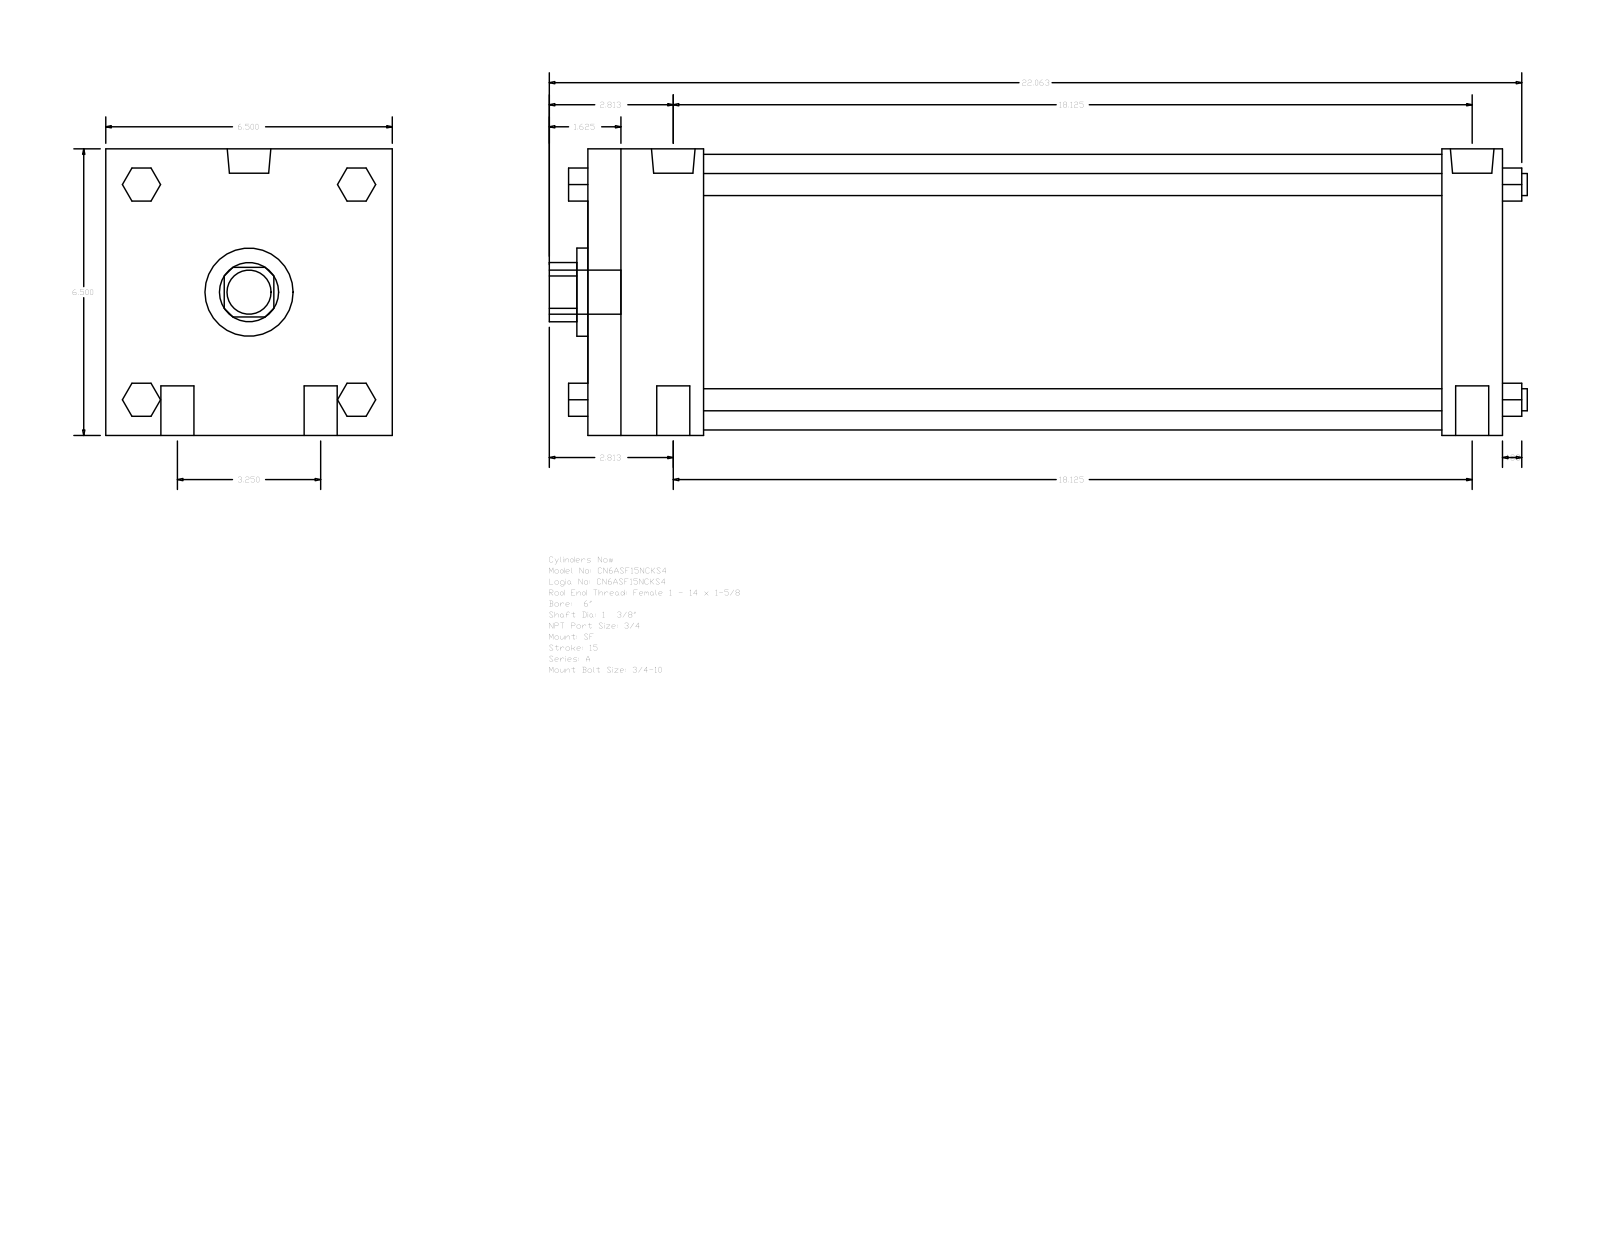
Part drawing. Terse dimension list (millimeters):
name: A_SF__0600_1.375
written by: GSSL Pune (CONFIG_CONTROL_DESIGN)
unit: mm
bodies: 0 solids, 124 faces (94 planar, 30 cylindrical, 0 other)
size: 563.56 × 165.1 × 165.1
holes: 1× ⌀34.92, 1× ⌀50.8, 1× ⌀158.75
bosses: 4× ⌀19.05, 4× ⌀12.7, 2× ⌀25.12, 2× ⌀15.08, 1× ⌀25.4
rounds: 1× R17.06
face distances: 165.1, 527.04, 492.12, 34.92, 66.67, 425.45, 460.37, 19.05, 61.97, 107.34
